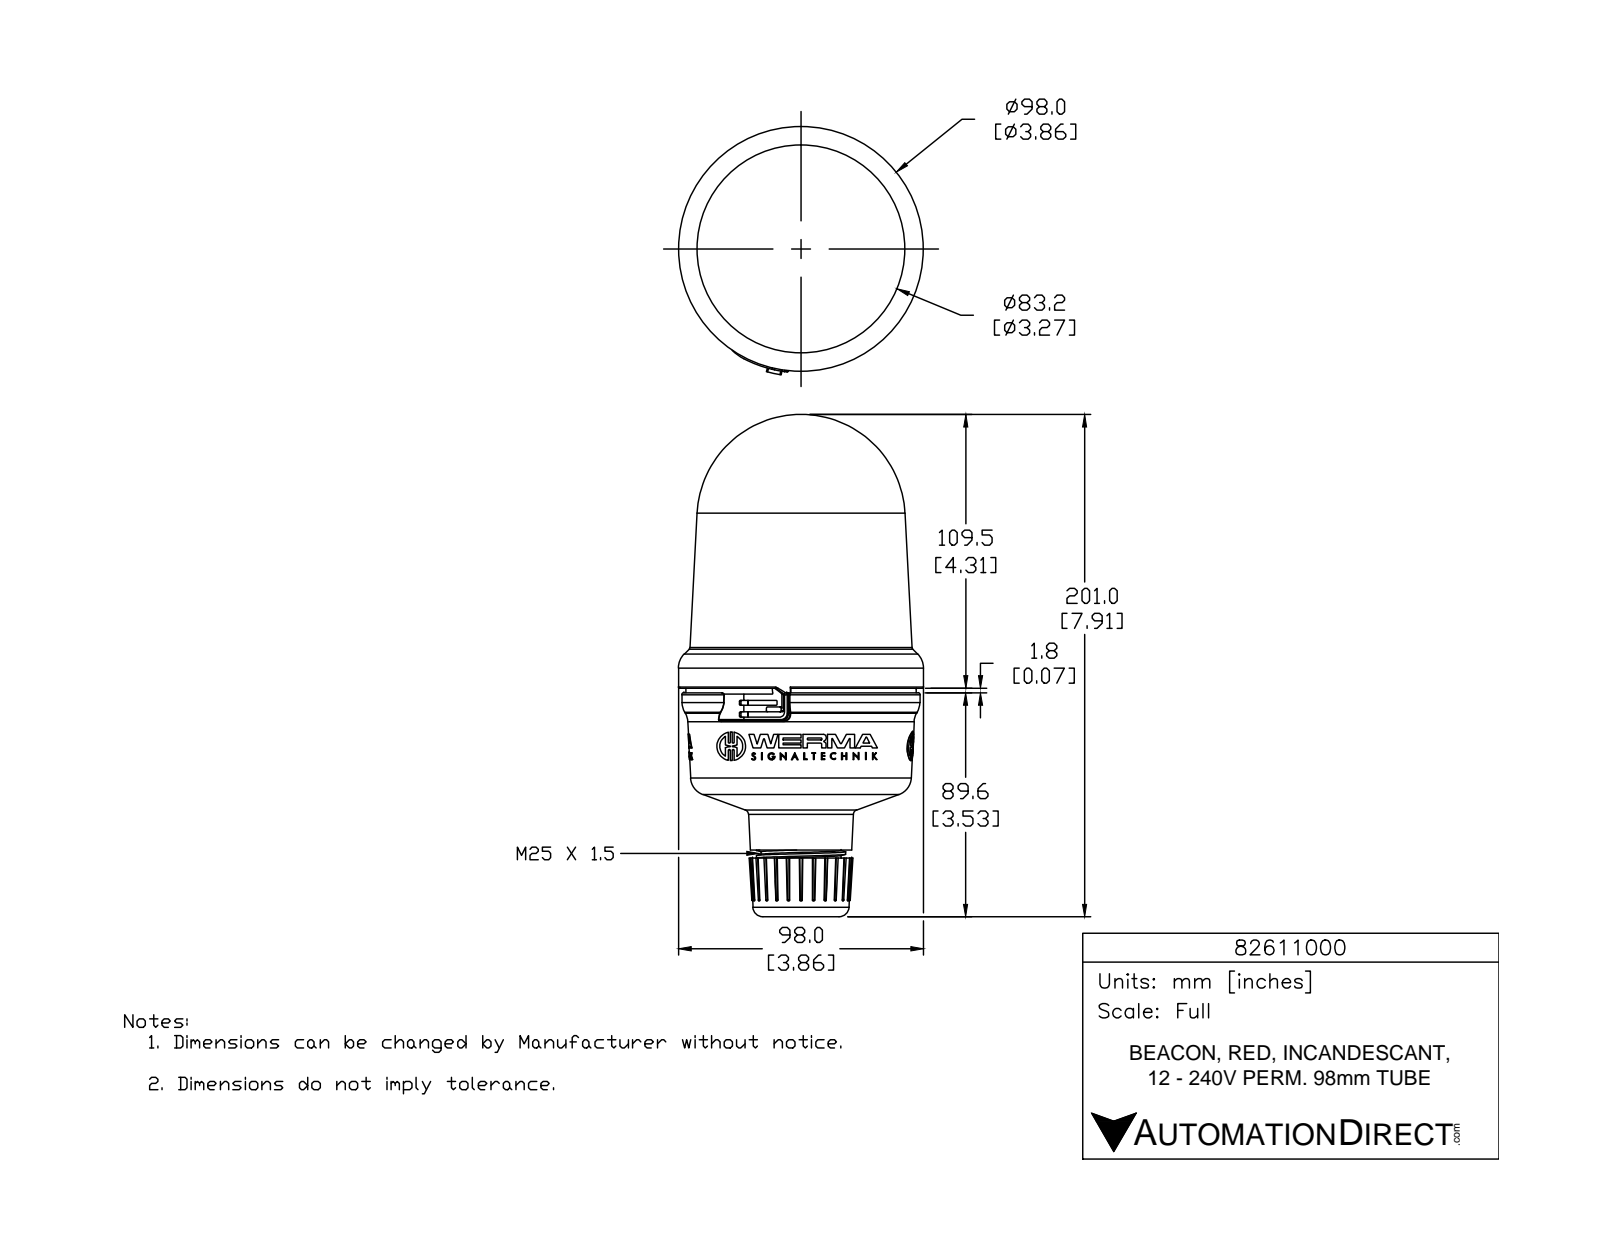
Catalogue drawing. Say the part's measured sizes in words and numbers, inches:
The part is named "82611000". Its 3-D file was written by "SolidWorks 2015 (AUTOMOTIVE_DESIGN)". It is 1 solid with 1006 faces: 554 planar, 189 cylindrical and 263 other. Overall it measures 7.914 by 3.912 by 3.858 inches. Its volume is 54.7 cubic inches and its surface area 91.39 square inches. Round holes: 3 of diameter 0.078, 1 of diameter 1.013, 1 of diameter 1.024. Round bosses or shafts: 3 of diameter 0.452, 3 of diameter 0.113, 1 of diameter 3.858, 1 of diameter 1.409, 1 of diameter 1.261. Partial cylindrical surfaces (rounded edges, fillets, slot ends): 12 of radius 0.02, 9 of radius 0.007, 6 of radius 0.007, 6 of radius 0.016, 6 of radius 0.016, 6 of radius 0.016, 6 of radius 0.262, 3 of radius 0.006. The main face-to-face distances are 2.214, 0.462, 2.676, 0.335, 0.127, 2.548, 2.603, 2.476, 2.141, 0.073.
